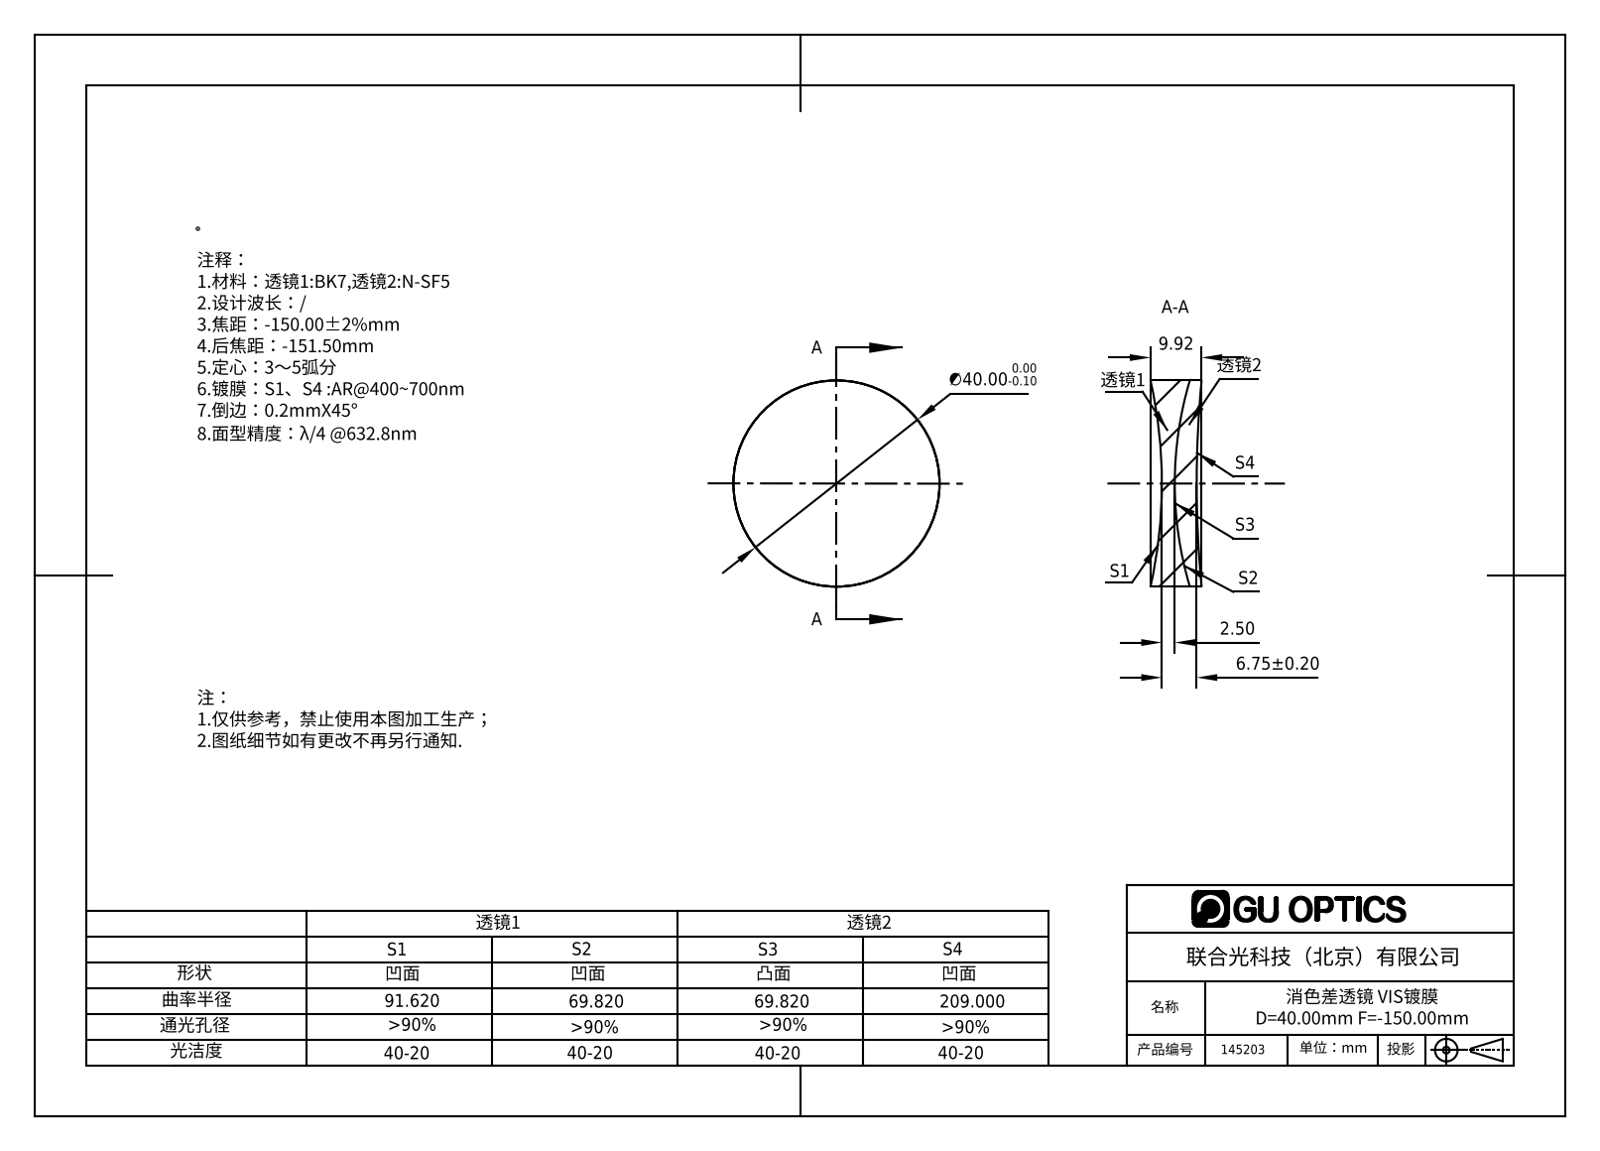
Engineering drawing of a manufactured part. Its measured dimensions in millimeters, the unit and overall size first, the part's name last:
Units: millimetres
Overall size (bounding box): 40 × 40 × 9.92
Round bosses / shafts (diameter × count): ⌀40 ×1
Volume: 10 467 mm³ · Surface area: 6 345 mm²
Bodies: 2 solids, 12 faces (0 planar, 4 cylindrical, 8 other)
Part name (STEP PRODUCT): 145203
STEP written by: SolidWorks 2016 (AUTOMOTIVE_DESIGN)
